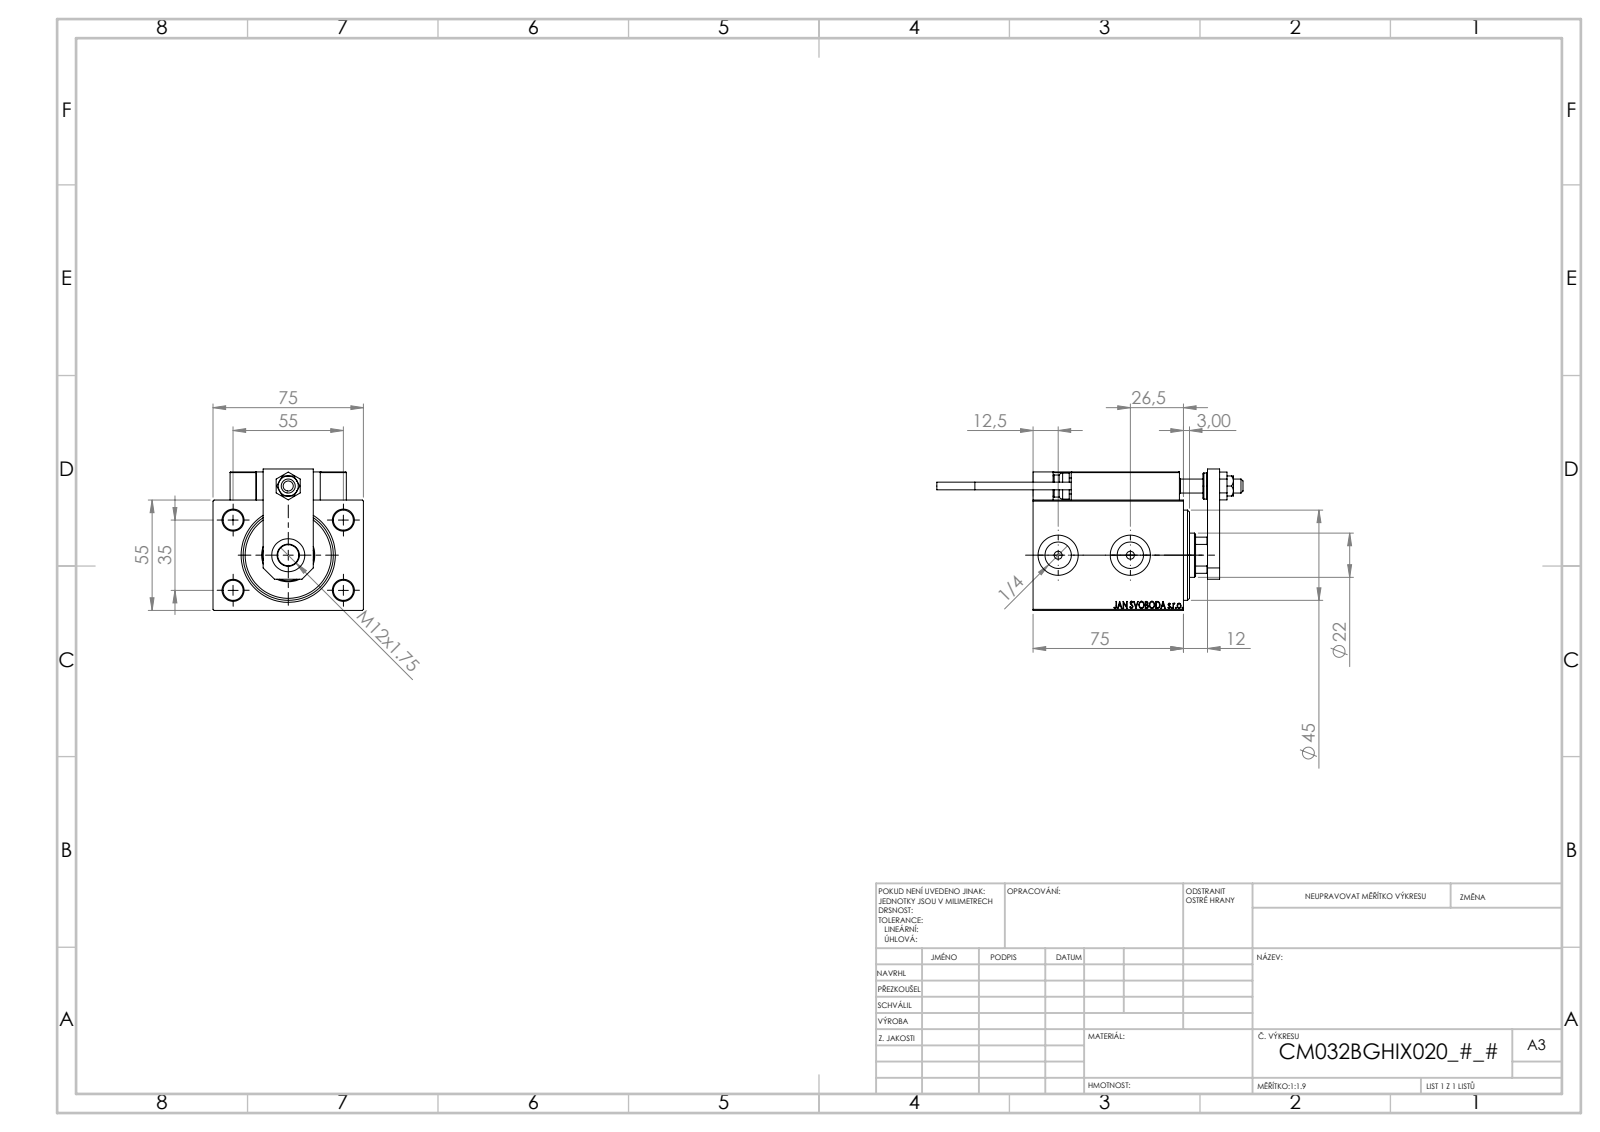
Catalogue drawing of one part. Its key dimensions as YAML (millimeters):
part_name: "NUT_D10; SWITCH X; ALLEN BOLT D5; V450CM_VC_B (+7 more)"
step_written_by: "SolidWorks 2019 (CONFIG_CONTROL_DESIGN)"
units: millimeters
bodies: {solids: 24, faces: 1318, planar: 561, cylindrical: 184, other: 573}
overall_size: [152.7, 75, 70.5]
volume: 337285
surface_area: 78969
round_holes:
  - {diameter: 4, count: 6}
  - {diameter: 8, count: 5}
  - {diameter: 3.2, count: 4}
  - {diameter: 10, count: 4}
  - {diameter: 5, count: 2}
  - {diameter: 13.16, count: 2}
  - {diameter: 20, count: 2}
  - {diameter: 7, count: 1}
  - {diameter: 10.5, count: 1}
  - {diameter: 16.5, count: 1}
  - {diameter: 22, count: 1}
  - {diameter: 25.5, count: 1}
round_bosses_or_shafts:
  - {diameter: 5, count: 2}
  - {diameter: 3.8, count: 2}
  - {diameter: 13, count: 1}
  - {diameter: 11, count: 1}
partial_cylinders:
  - {radius: 0.3, count: 30}
  - {radius: 3, count: 2}
  - {radius: 10.5, count: 1}
face_to_face_distances: [55, 75, 10, 12, 14, 7, 69, 65, 25, 20]
hole_center_spacings: [32.6, 11.37, 20, 27.07, 29.59, 29.69, 32.33, 34.83]
